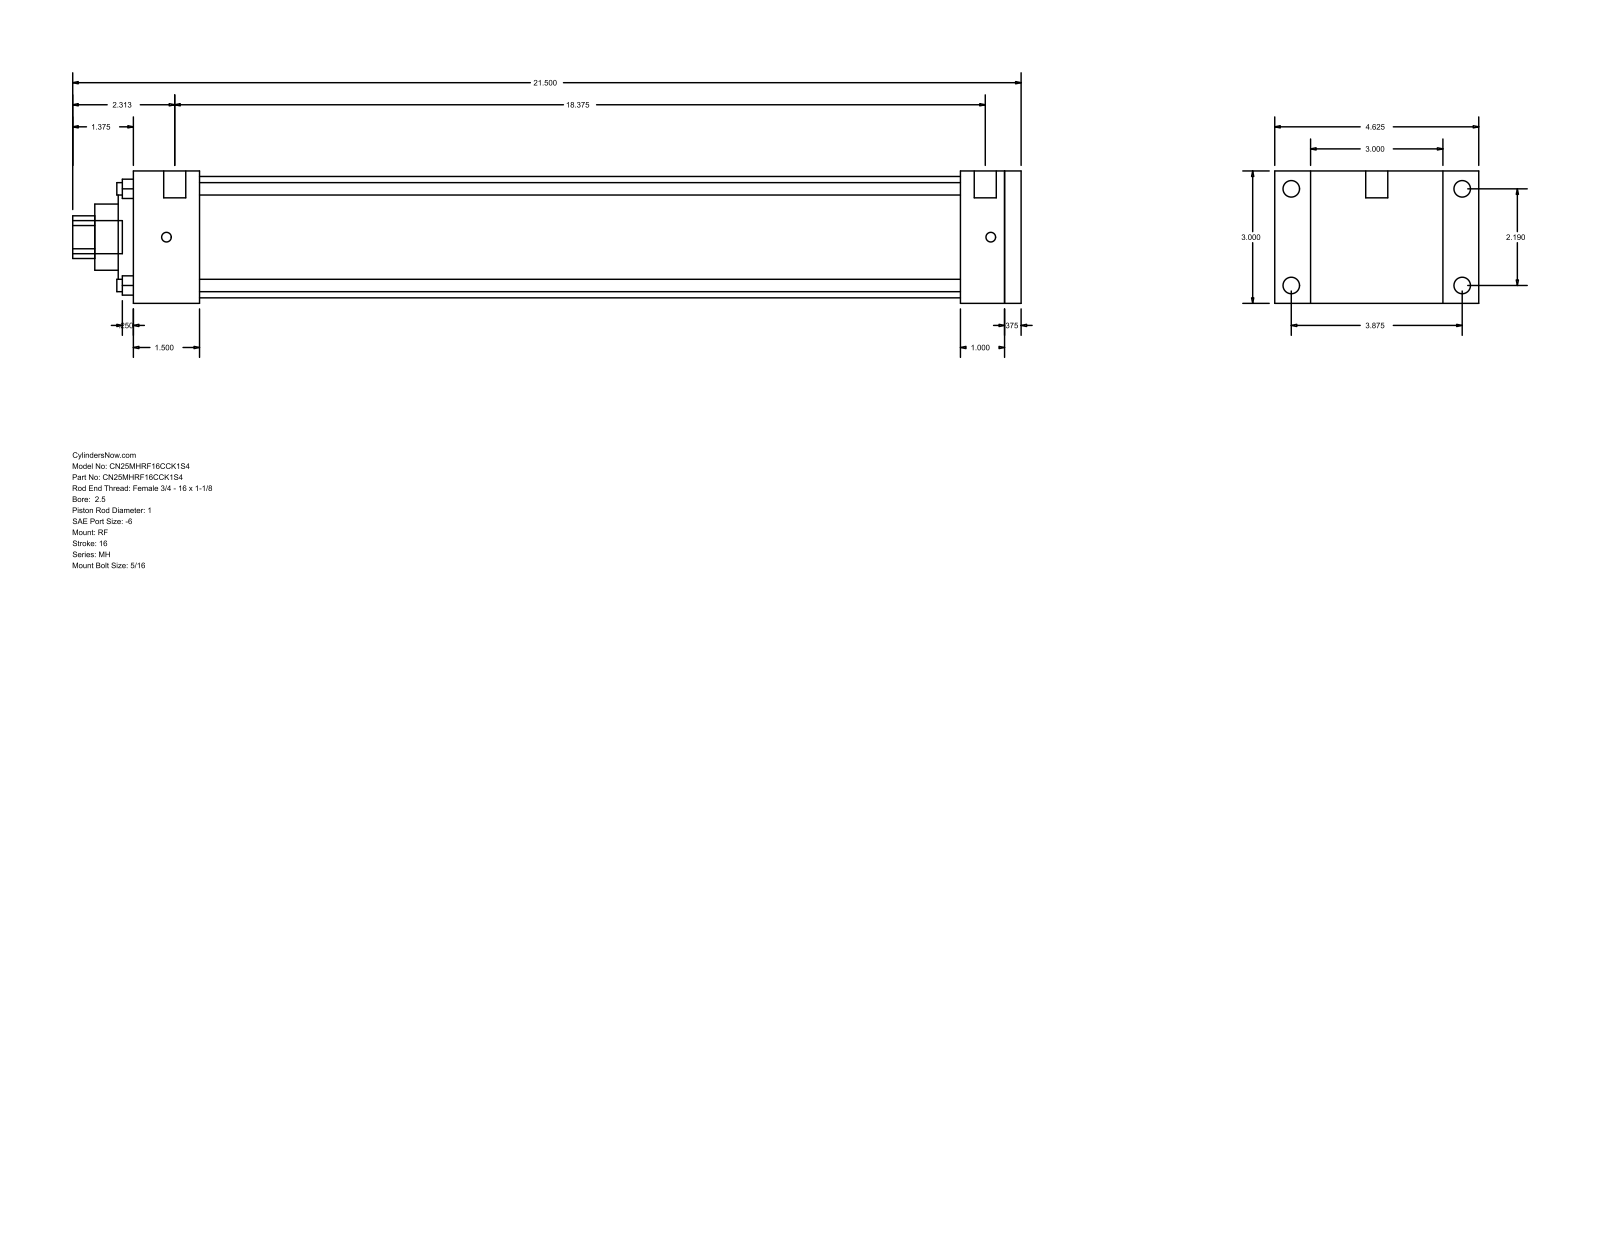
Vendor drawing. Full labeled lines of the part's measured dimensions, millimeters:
Part name (STEP PRODUCT): MH_RF__0250_1
STEP written by: GSSL Pune (CONFIG_CONTROL_DESIGN)
Units: millimetres
Bodies: 0 solids, 94 faces (65 planar, 29 cylindrical, 0 other)
Overall size (bounding box): 546.1 × 117.47 × 76.2
Round holes (diameter × count): ⌀7.14 ×4, ⌀25.4 ×1, ⌀38.1 ×1, ⌀60.33 ×1, ⌀69.85 ×1
Round bosses / shafts (diameter × count): ⌀9.53 ×4, ⌀5.56 ×4, ⌀12.7 ×2, ⌀19.05 ×1
Partial cylindrical surfaces — rounded edges, fillets, slot ends (radius × count): R12.29 ×1
Main face-to-face distances: 76.2, 9.52, 511.18, 501.66, 25.4, 34.92, 476.26, 38.11, 438.15, 463.55
Hole centre spacings: 39.33, 55.62, 78.66
